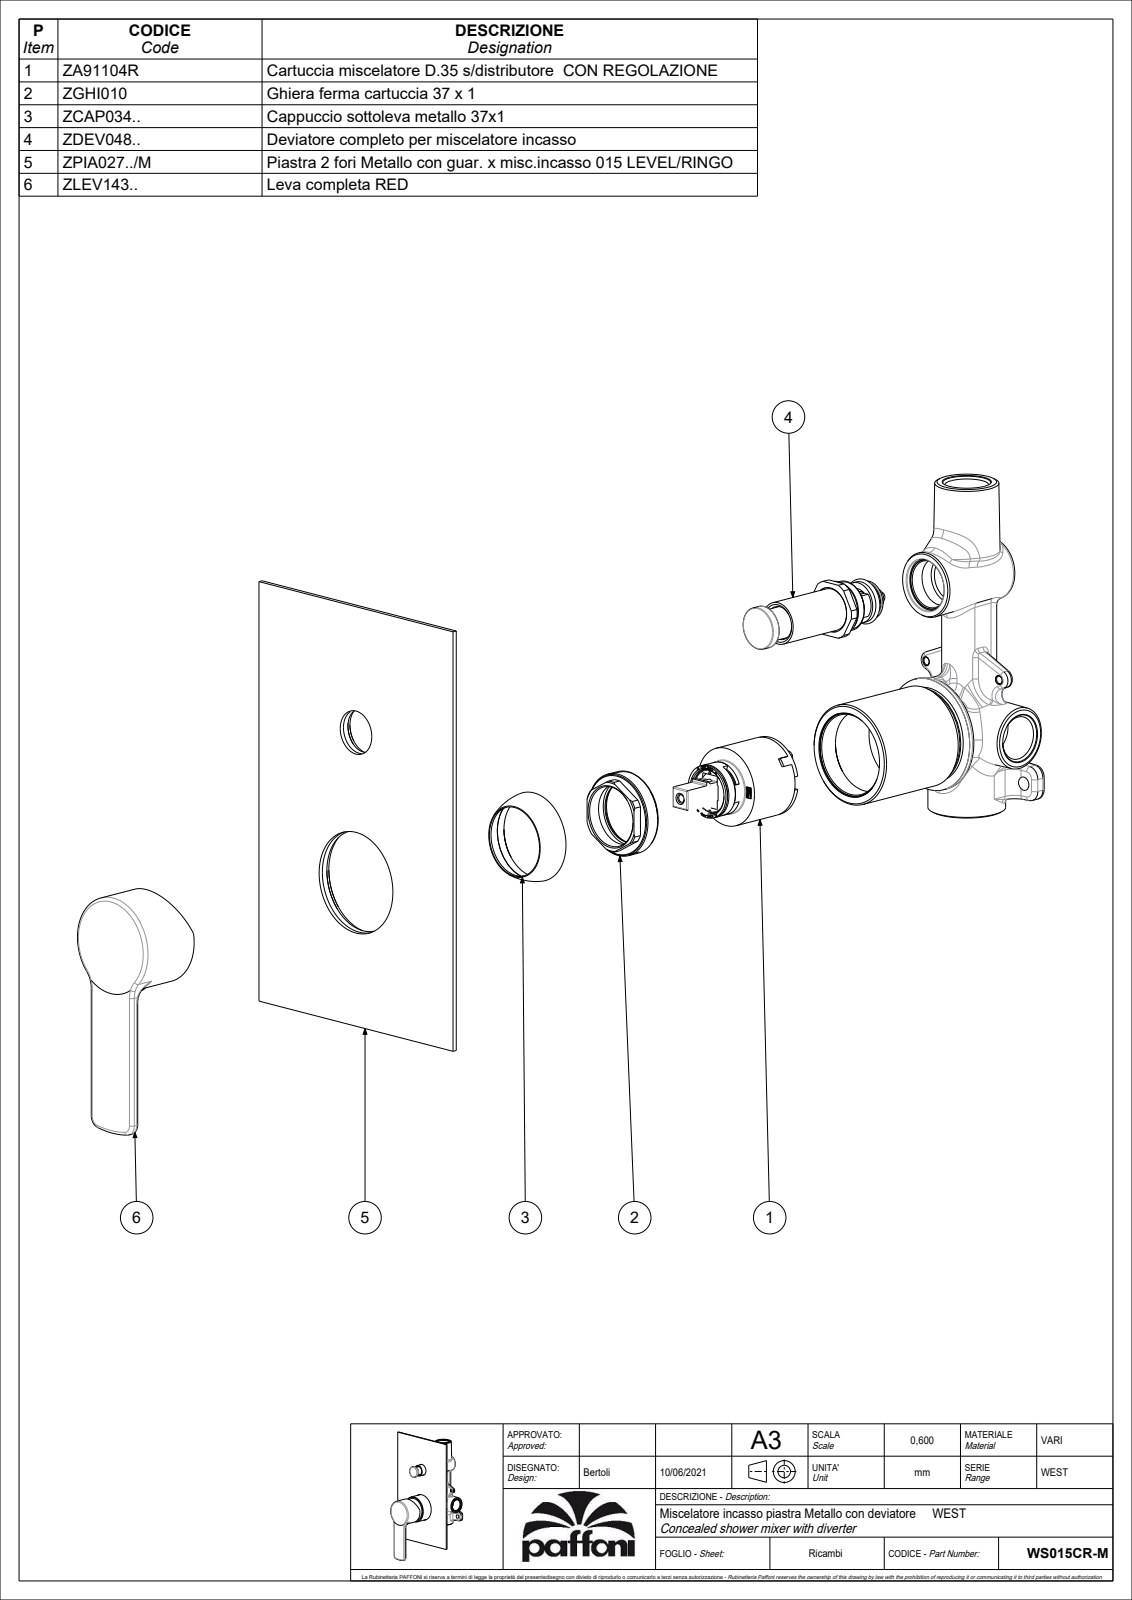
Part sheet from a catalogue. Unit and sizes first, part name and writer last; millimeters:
Units: millimetres
Overall size (bounding box): 210 × 120 × 59.08
Round holes (diameter × count): ⌀3.3 ×2, ⌀4 ×2, ⌀19.5 ×2, ⌀3 ×1, ⌀4.5 ×1, ⌀5 ×1, ⌀10.5 ×1, ⌀14.8 ×1, ⌀19.9 ×1, ⌀26.8 ×1, ⌀29 ×1, ⌀31 ×1
Round bosses / shafts (diameter × count): ⌀44.8 ×1, ⌀43 ×1, ⌀35 ×1, ⌀23.5 ×1, ⌀23.4 ×1, ⌀21.8 ×1, ⌀18.7 ×1, ⌀18.6 ×1
Partial cylindrical surfaces — rounded edges, fillets, slot ends (radius × count): R0.5 ×45, R0.15 ×11, R0.3 ×4, R1.5 ×4, R1 ×2, R5 ×2, R10 ×2, R7 ×1
Main face-to-face distances: 2, 54.1, 52.1, 4.5, 58.6, 56.6, 5.5, 16.5, 14.5, 55.5
Hole centre spacings: 12.5, 68
Volume: 92 698 mm³ · Surface area: 81 750 mm²
Bodies: 5 solids, 1009 faces (568 planar, 244 cylindrical, 197 other)
Part name (STEP PRODUCT): WS015CR-M
STEP written by: CREO PARAMETRIC BY PTC INC, 2020044 (CONFIG_CONTROL_DESIGN)
